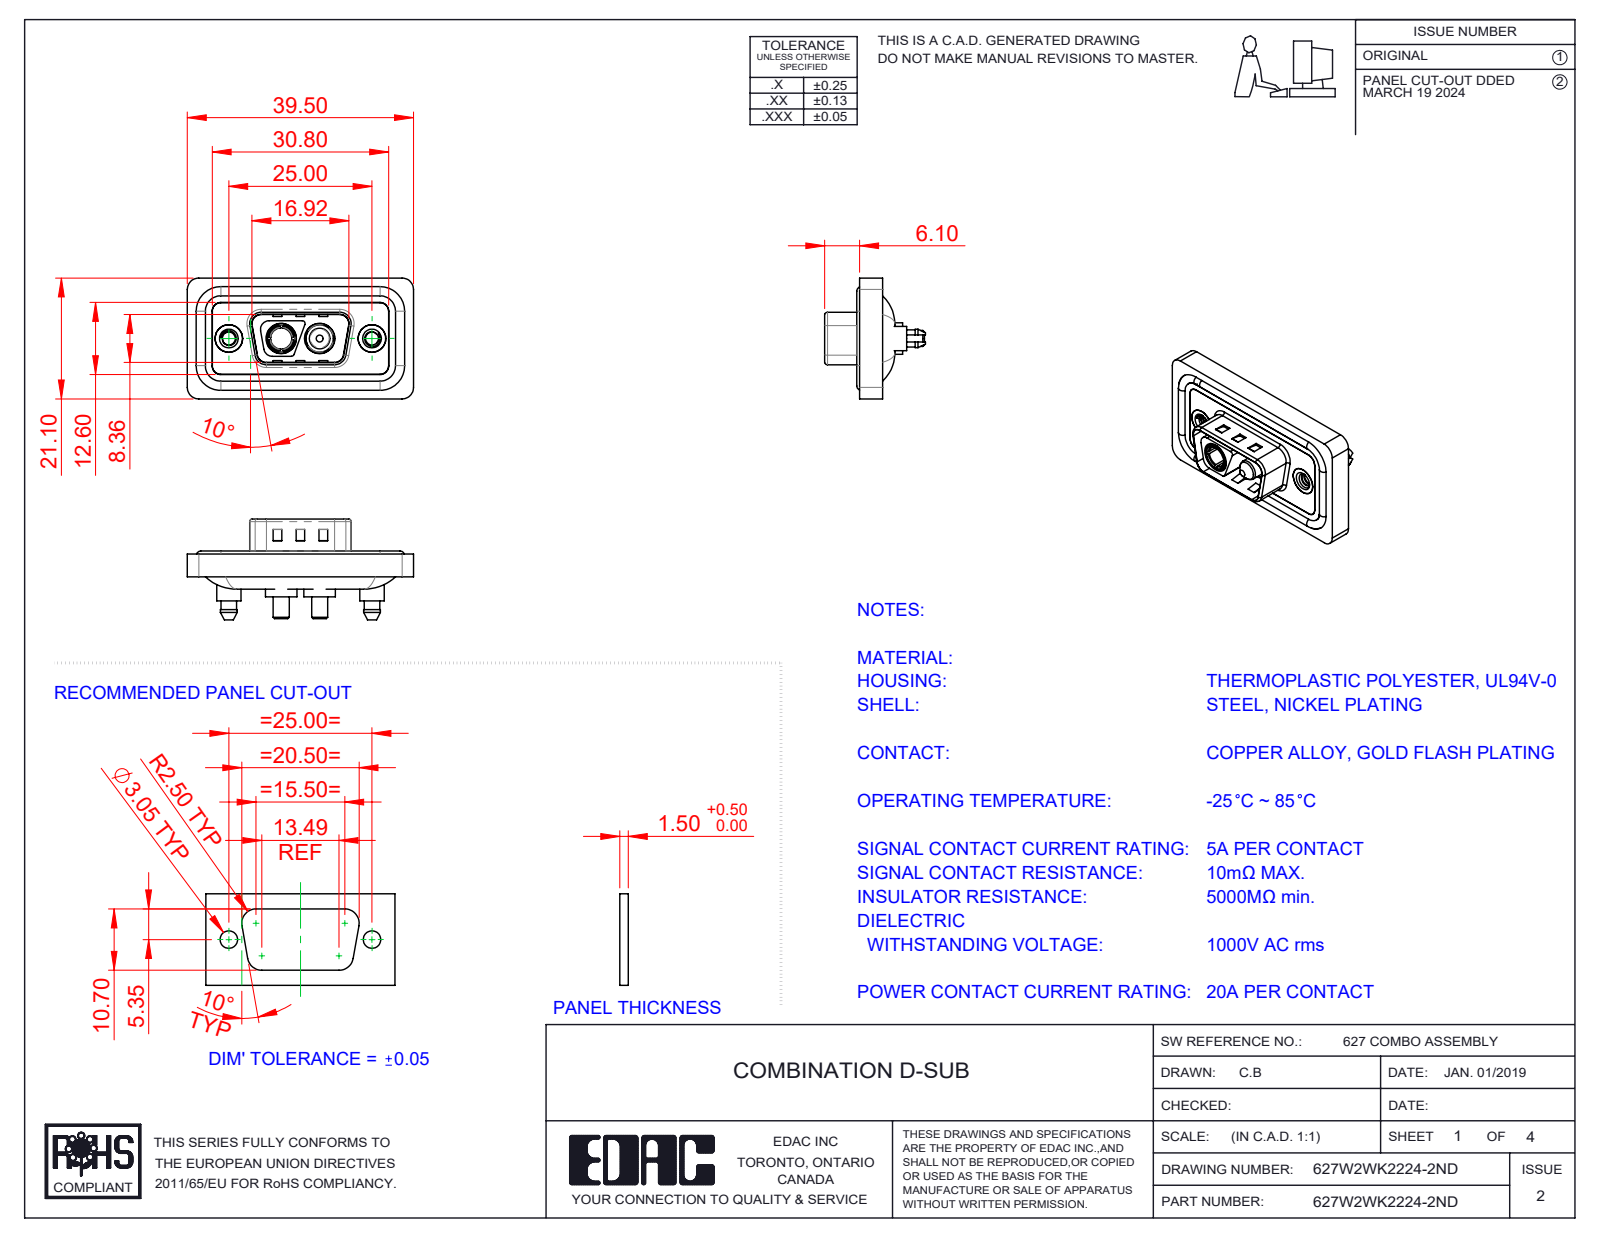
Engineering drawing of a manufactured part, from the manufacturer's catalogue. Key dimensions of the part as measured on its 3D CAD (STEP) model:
Part name (STEP PRODUCT): Power Pin_20A S; 627Combo Threaded Boardlock_5; 627Combo Shell Front_09 Contacts; 627Combo Shell Rear_09 Contacts (+5 more)
STEP written by: SolidWorks 2023 (CONFIG_CONTROL_DESIGN)
Units: millimetres
Bodies: 11 solids, 592 faces (205 planar, 267 cylindrical, 120 other)
Overall size (bounding box): 39.5 × 21.1 × 17.6
Volume: 4 689 mm³ · Surface area: 7 678 mm²
Round holes (diameter × count): ⌀2.26 ×2, ⌀4 ×2, ⌀4.8 ×2, ⌀4.85 ×2, ⌀5 ×2, ⌀5.3 ×2, ⌀3.7 ×1
Round bosses / shafts (diameter × count): ⌀1.6 ×4, ⌀5.5 ×2, ⌀5.4 ×2, ⌀5.2 ×2, ⌀4.9 ×2, ⌀4.75 ×2, ⌀4.25 ×2, ⌀3.75 ×2
Partial cylindrical surfaces — rounded edges, fillets, slot ends (radius × count): R1.5 ×26, R2 ×18, R0.5 ×10, R1.6 ×10, R0.25 ×4, R0.6 ×4, R0.65 ×4, R0.9 ×4
Main face-to-face distances: 0.4, 1.1, 2.9, 3.1, 0.5, 1.6, 1.5, 4, 1.8, 3.2
Hole centre spacings: 9.14, 15.86, 6.72, 25
